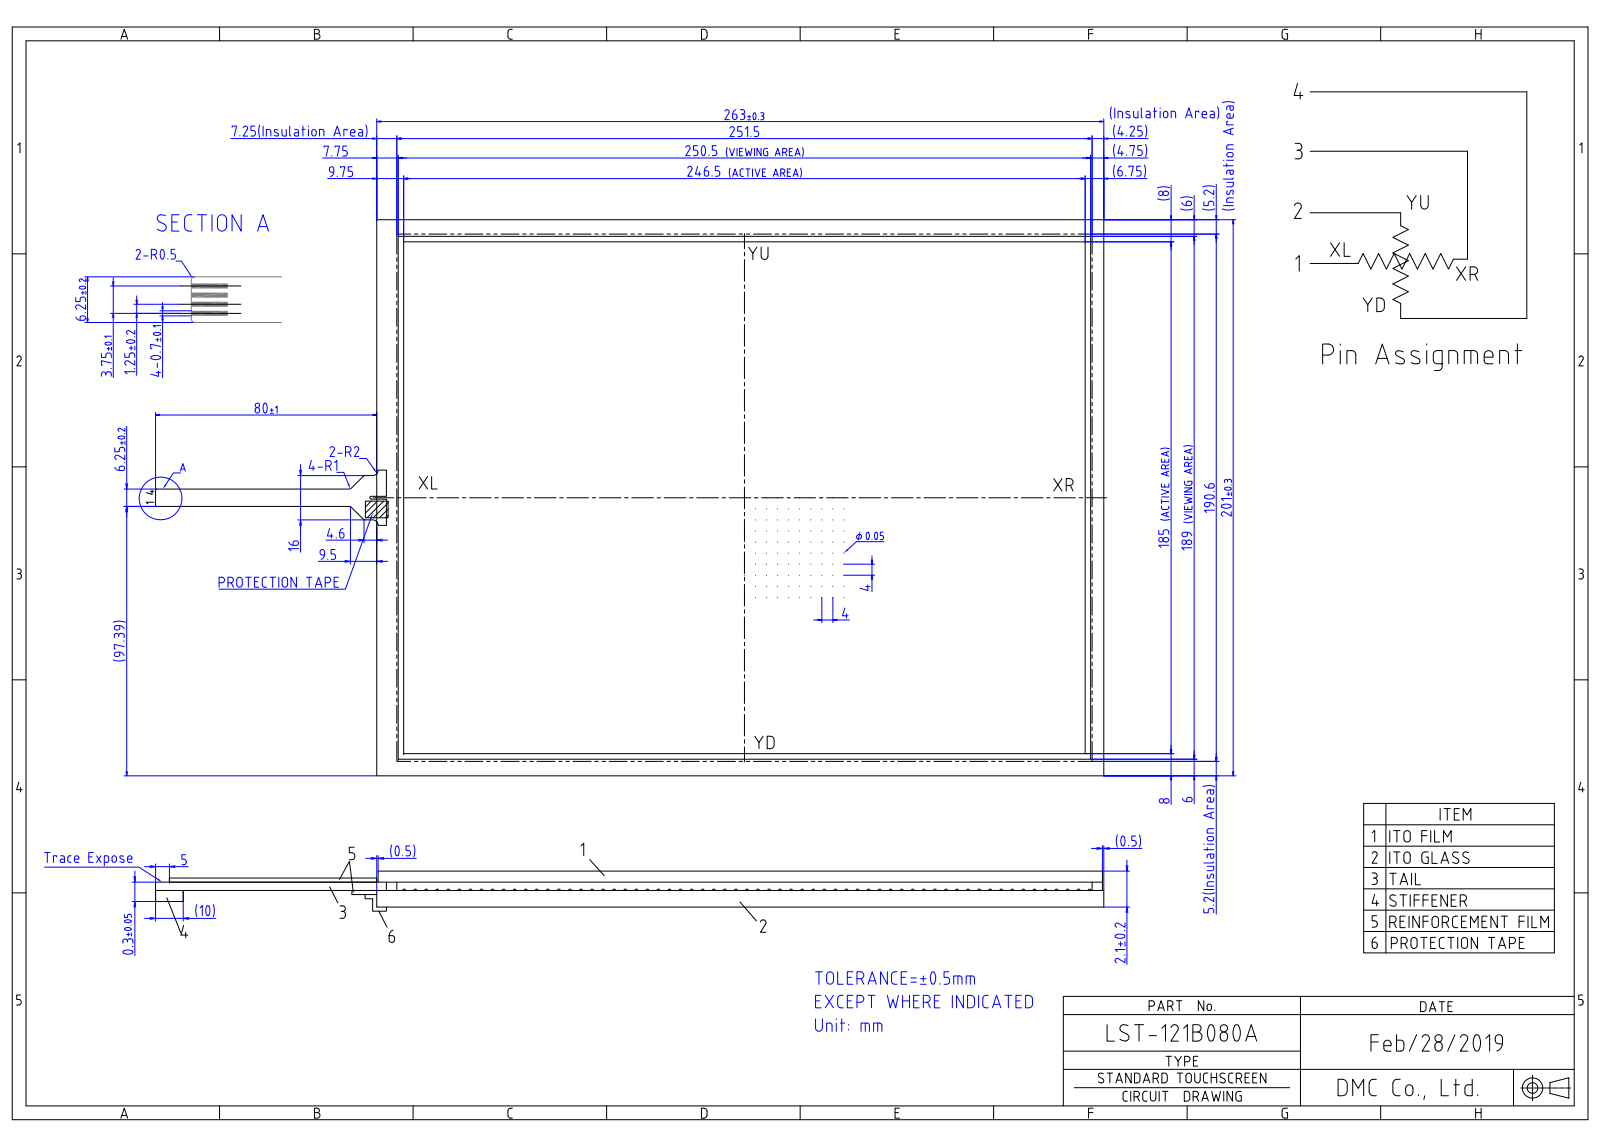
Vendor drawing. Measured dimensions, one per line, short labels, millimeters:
name: LST-121B080A
written by: Autodesk Inventor 2020 (CONFIG_CONTROL_DESIGN)
unit: mm
bodies: 1 solid, 51 faces (45 planar, 6 cylindrical, 0 other)
size: 343 × 201 × 2.1
volume: 110 909 mm³; area: 108 982 mm²
rounds: 4× R1, 2× R0.2
face distances: 2.1, 2, 201, 1.91, 1.81, 263, 1.51, 0.4, 0.49, 0.59
